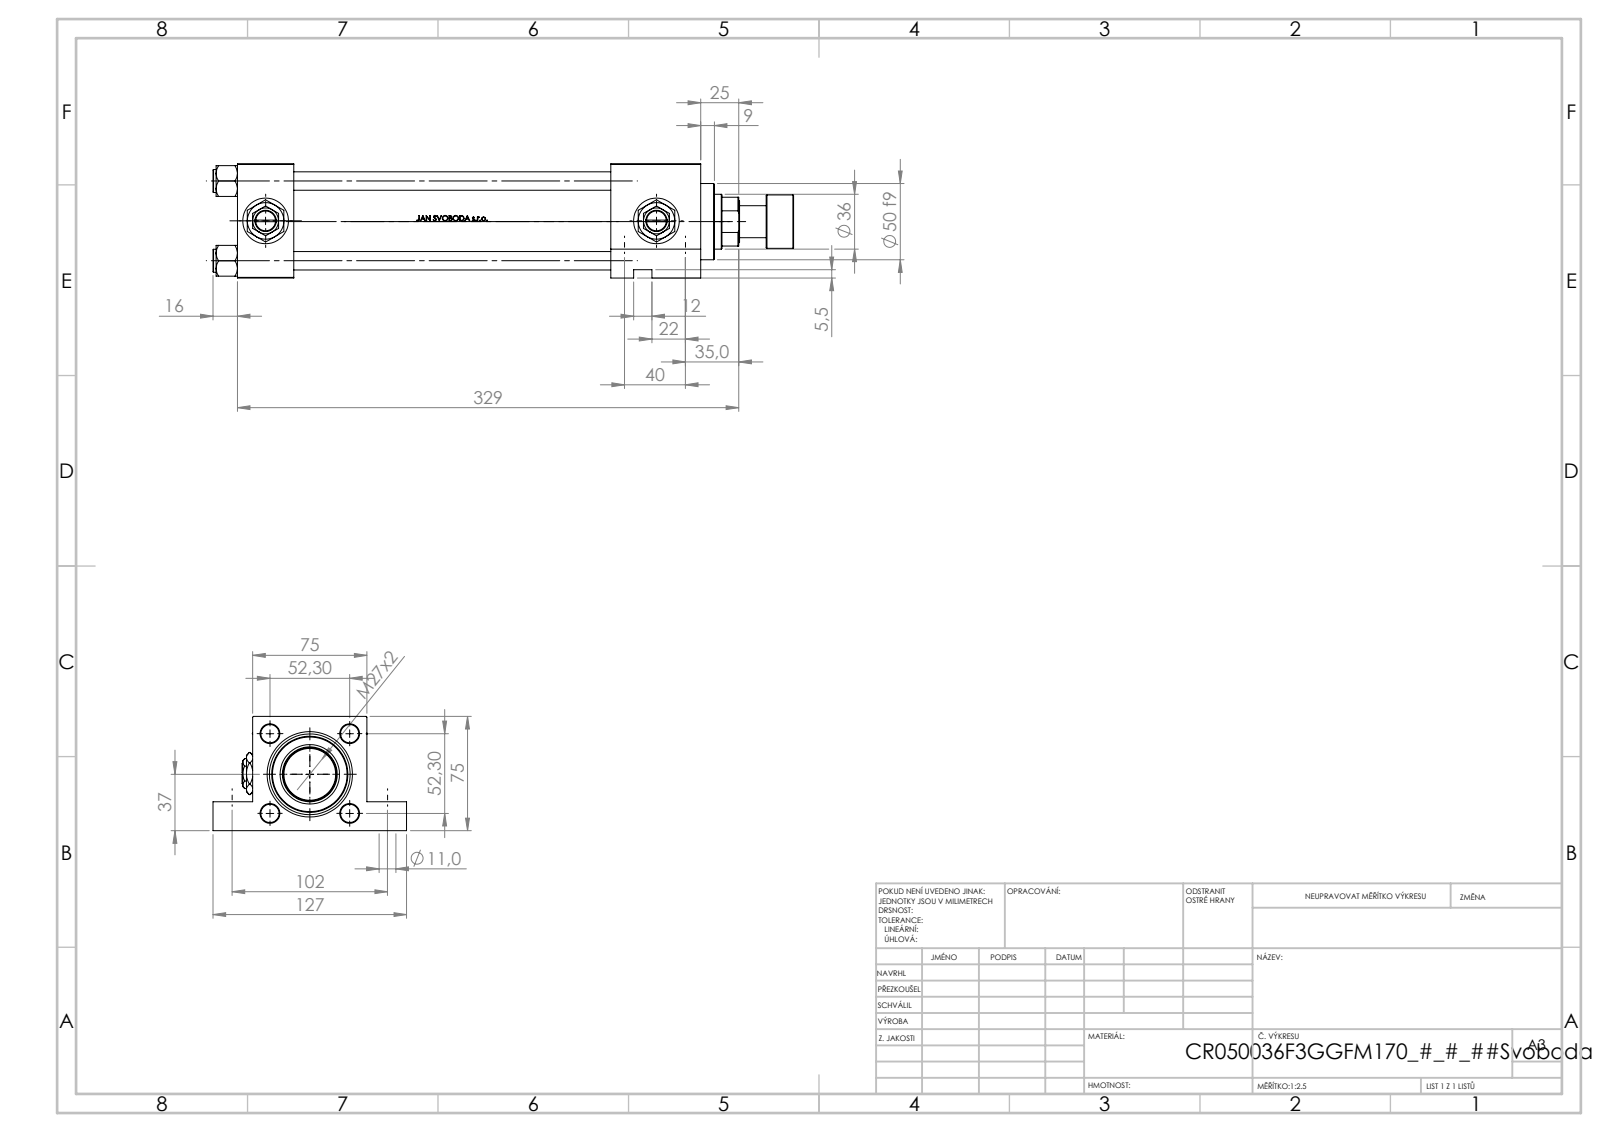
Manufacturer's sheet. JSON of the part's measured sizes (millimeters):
{"part_name": "V215CR_F_Body; NUT_M5_F; V215_VC_A; V215CR_VCP_F (+3 more)", "step_written_by": "SolidWorks 2019 (CONFIG_CONTROL_DESIGN)", "units": "millimeters", "bodies": {"solids": 14, "faces": 1216, "planar": 488, "cylindrical": 140, "other": 588}, "overall_size": [381, 127, 75], "volume_mm3": 1049000, "surface_area_mm2": 264076, "round_holes": [[11, 4], [12, 4], [20.96, 4], [30, 4], [7, 3], [25.5, 1], [36, 1], [39, 1], [41, 1], [53, 1]], "round_bosses_or_shafts": [[15, 4], [56, 1], [50, 1], [35, 1], [21, 1]], "face_to_face_distances": [75, 37, 245, 208, 59, 304, 267, 19, 56, 74.8], "hole_center_spacings": [52.3, 36.63, 37.34, 40, 51.62, 60.21, 73.96, 102]}
